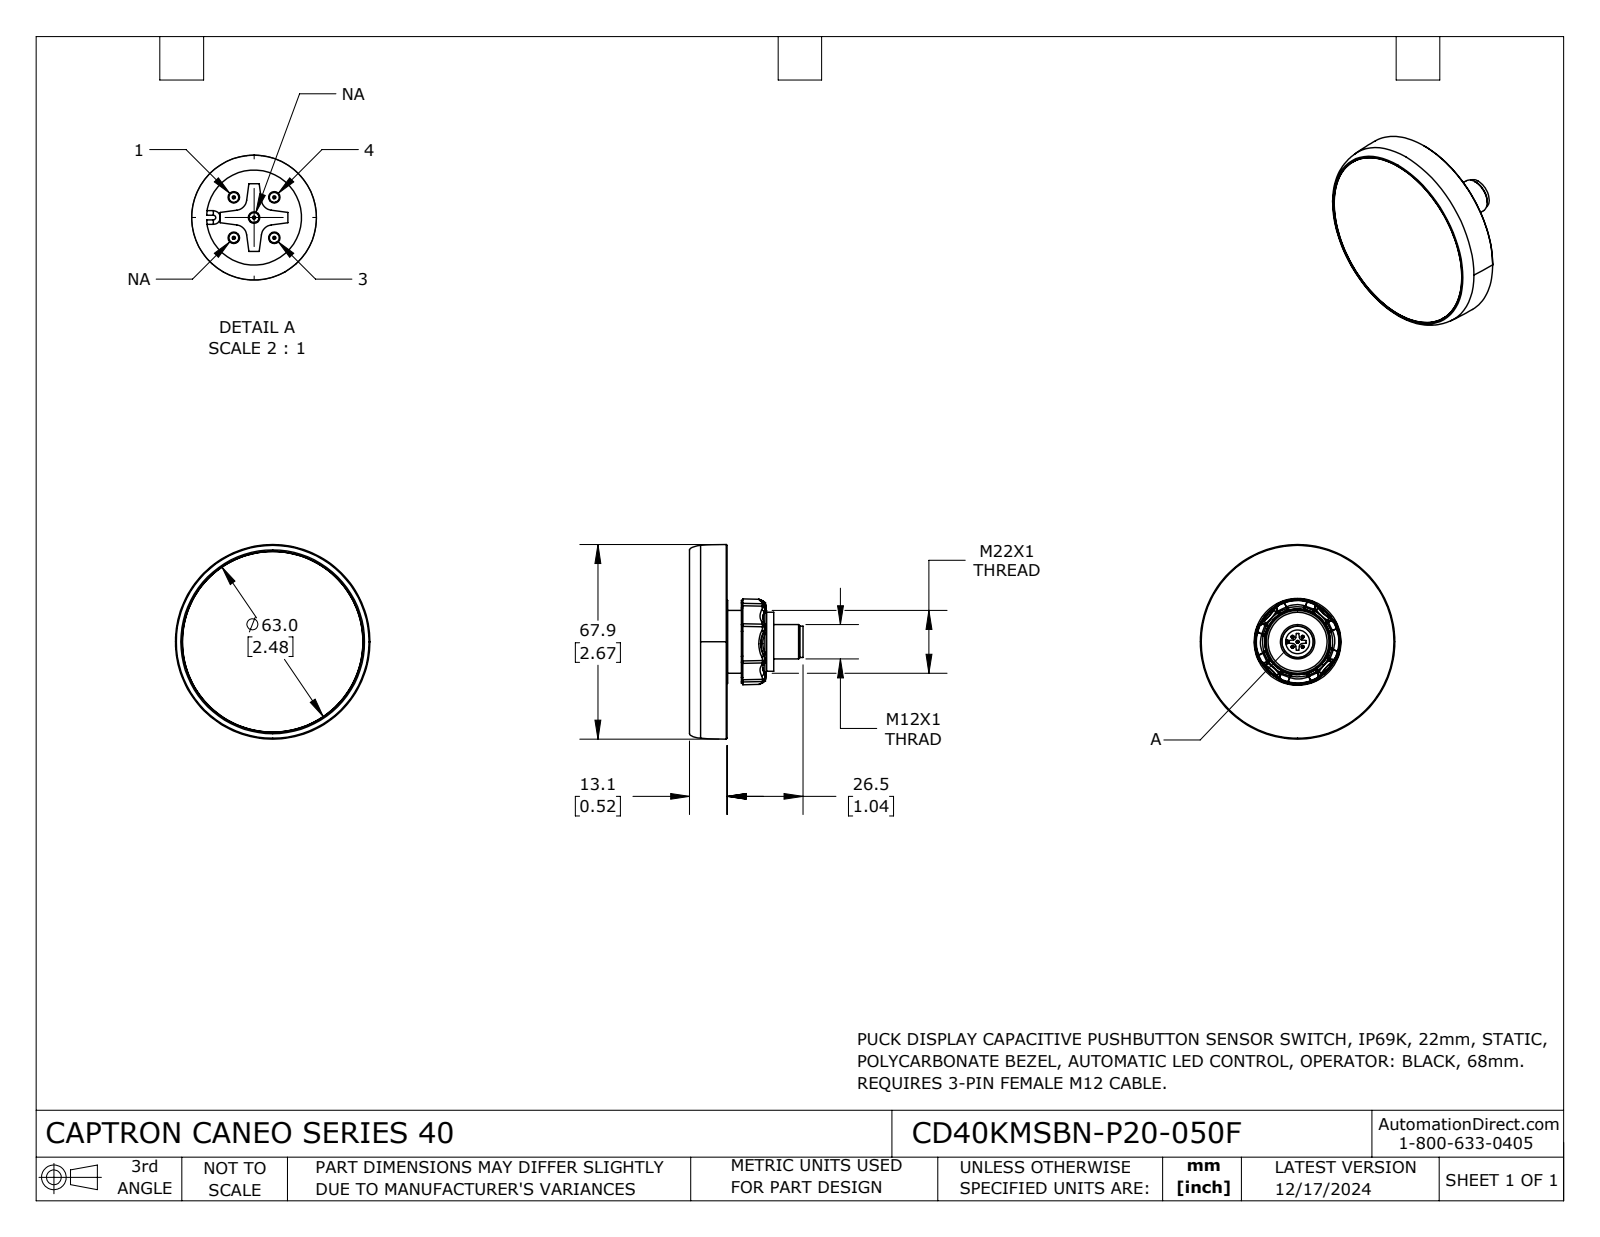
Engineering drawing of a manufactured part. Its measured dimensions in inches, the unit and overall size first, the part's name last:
Units: inches
Overall size (bounding box): 2.673 × 2.673 × 1.559
Round holes (diameter × count): ⌀0.327 ×1, ⌀0.827 ×1, ⌀0.927 ×1, ⌀1.193 ×1, ⌀2.484 ×1
Round bosses / shafts (diameter × count): ⌀0.039 ×5, ⌀2.48 ×1, ⌀0.862 ×1, ⌀0.811 ×1, ⌀0.472 ×1, ⌀0.429 ×1
Partial cylindrical surfaces — rounded edges, fillets, slot ends (radius × count): R0.295 ×8, R0.039 ×4, R0.689 ×4, R0.016 ×2, R0.024 ×1
Main face-to-face distances: 0.516, 0.02, 0.496, 0.642, 0.661, 1.157, 0.217, 0.713, 0.197, 0.659
Volume: 3.397 in³ · Surface area: 23.2 in²
Bodies: 3 solids, 420 faces (62 planar, 50 cylindrical, 308 other)
Part name (STEP PRODUCT): CD40KMSBN-P20-050F
STEP written by: SolidWorks 2024 (CONFIG_CONTROL_DESIGN)
